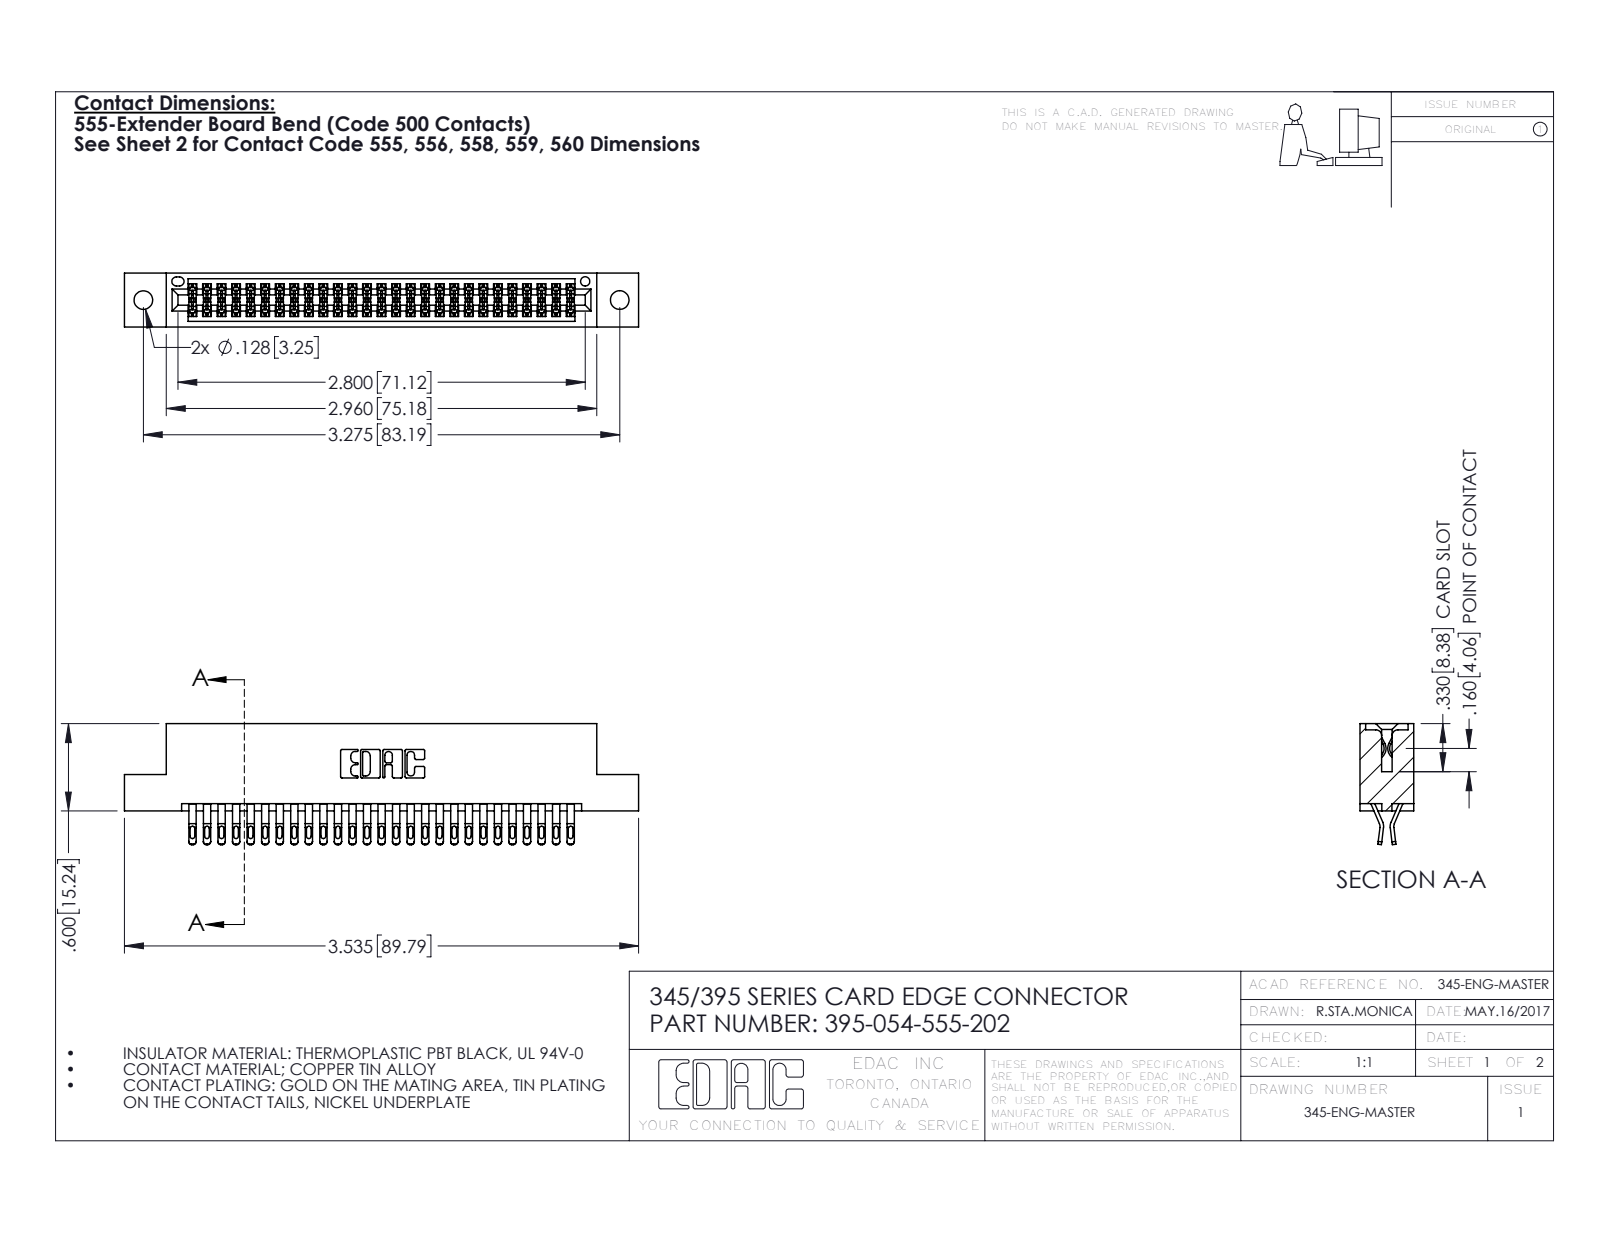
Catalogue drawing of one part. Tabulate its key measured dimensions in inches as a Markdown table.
| quantity | value |
| --- | --- |
| part name | 345-292-001_555 Tail; 395-054-555-202; 345 Part_Flush Mounting Lugs - 0.128 Dia |
| STEP written by | SolidWorks 2016 (CONFIG_CONTROL_DESIGN) |
| units | inches |
| bodies | 55 solids, 3150 faces (1754 planar, 1396 cylindrical, 0 other) |
| overall size | 3.535 × 0.832 × 0.37 |
| volume | 0.531 in³ |
| surface area | 19.91 in² |
| round holes (diameter × count) | 0.128 × 2, 0.064 × 1 |
| partial cylindrical surfaces (radius × count) | 0.016 × 135, 0.02 × 108, 0.006 × 81, 0.01 × 22, 0.007 × 6, 0.031 × 6, 0.026 × 3, 0.01 × 2 |
| main face-to-face distances | 0.298, 0.072, 0.2, 0.37, 0.025, 0.098, 0.272, 0.225, 0.175, 0.149 |
| hole center spacings | 0.27, 3.04, 3.275 |
